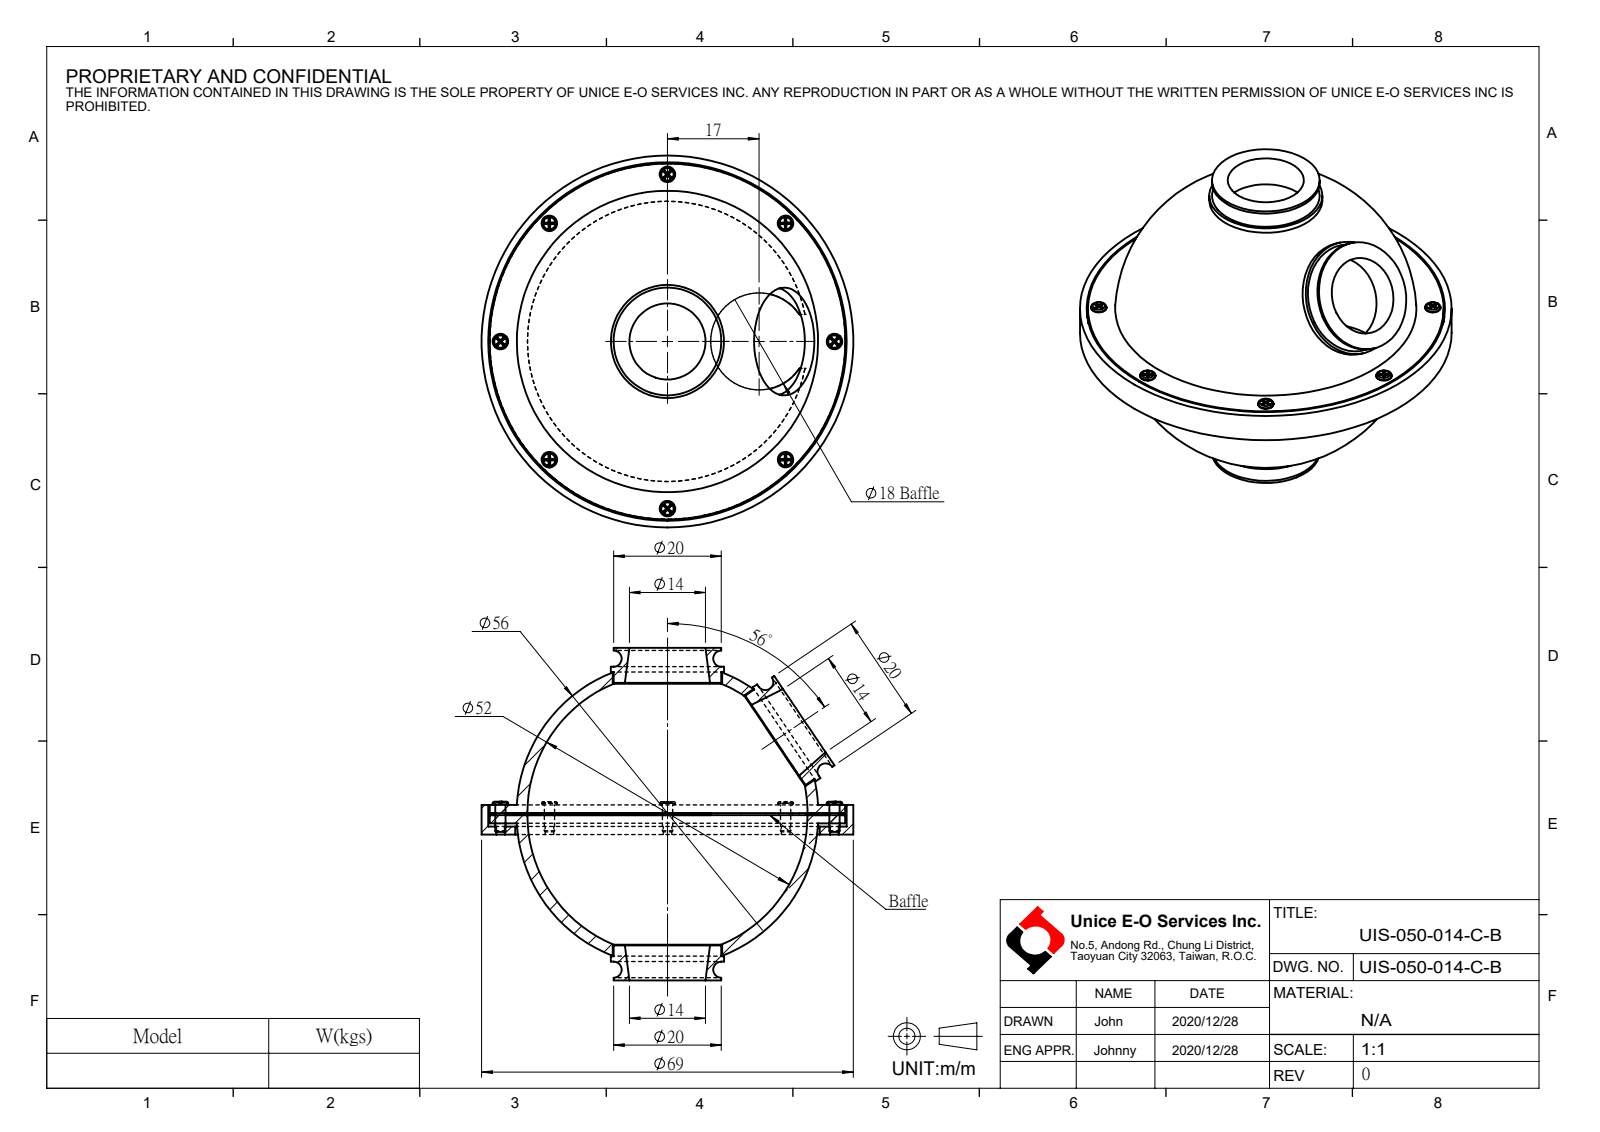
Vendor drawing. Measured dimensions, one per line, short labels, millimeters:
name: UIS-050-014-C-B
written by: SolidWorks 2020 (CONFIG_CONTROL_DESIGN)
unit: mm
bodies: 0 solids, 182 faces (86 planar, 38 cylindrical, 58 other)
size: 69 × 69 × 61.71
holes: 8× ⌀1.6, 1× ⌀56.5, 1× ⌀66.5
bosses: 2× ⌀21, 2× ⌀20, 1× ⌀69, 1× ⌀66, 1× ⌀20.3
face distances: 4, 1.5, 5.5, 2.1, 0.6, 1.9, 3.4, 2.5, 29.15, 32.55
hole spacings: 23.73, 31, 43.84, 57.28, 62
